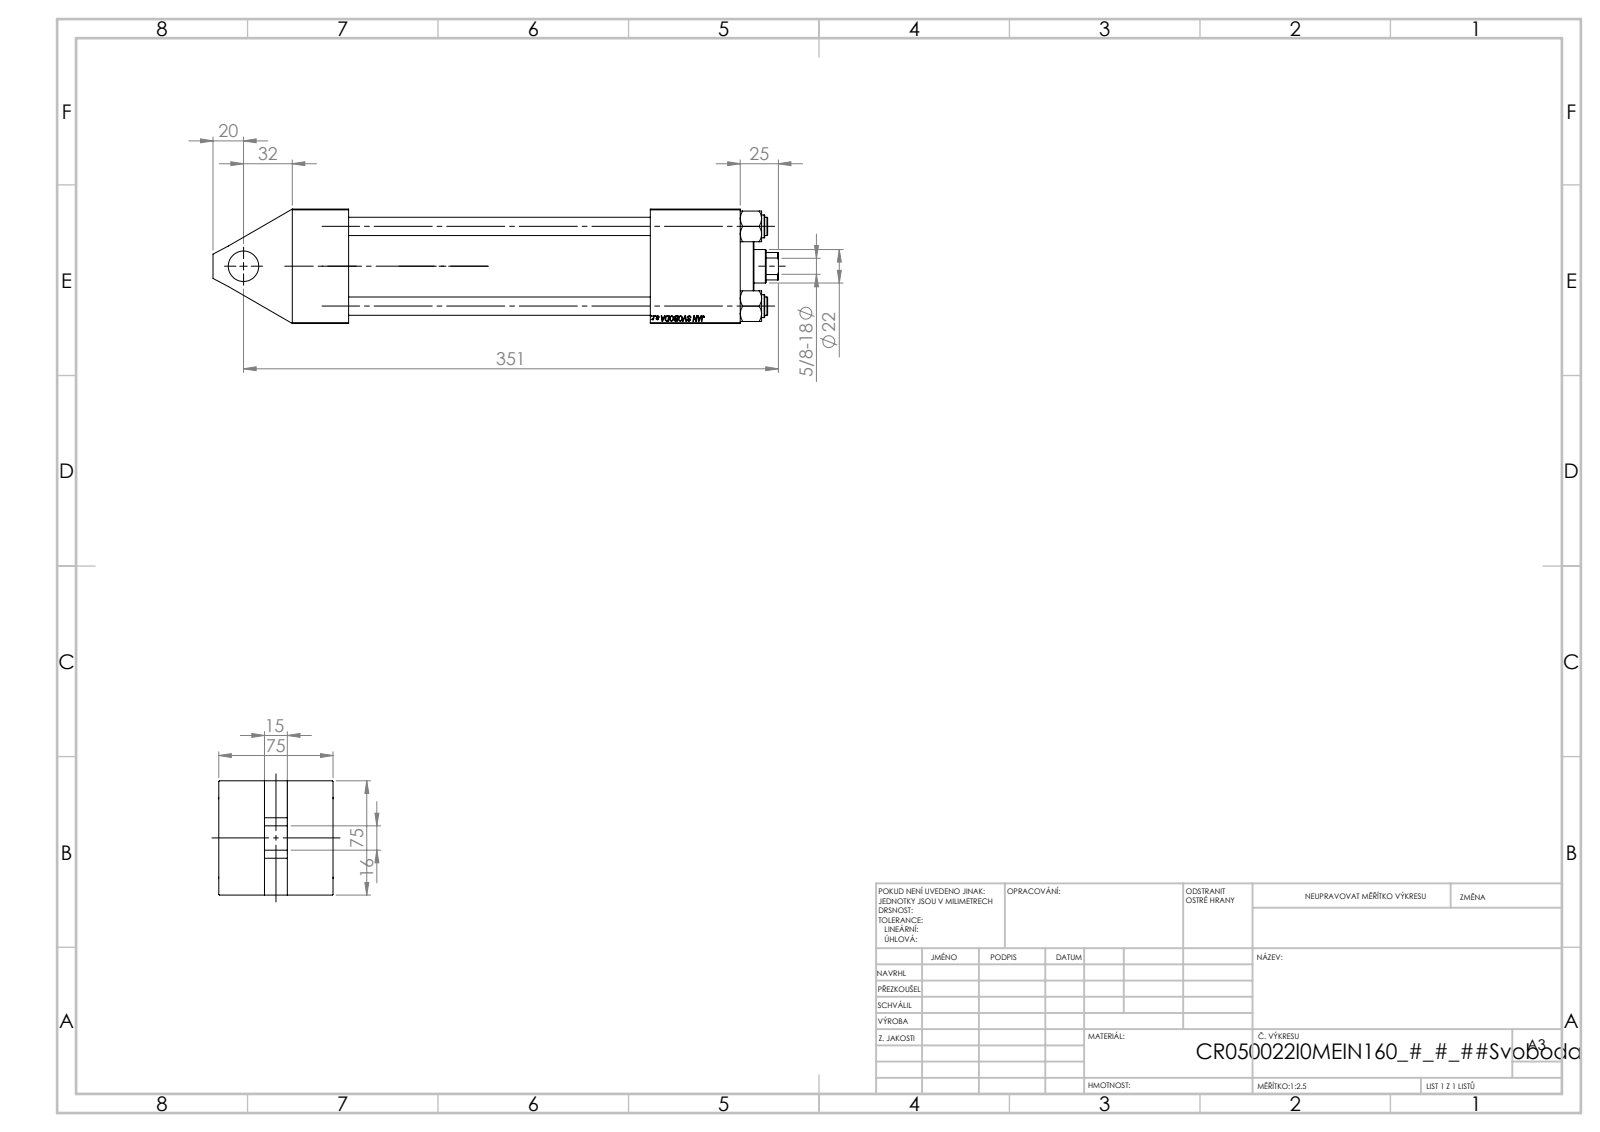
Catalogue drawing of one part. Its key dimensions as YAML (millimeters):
part_name: "V215CR_TYCINKA_I; V215_VC_A; V215CR_I_Body; V215CR_VCP_I (+1 more)"
step_written_by: "SolidWorks 2019 (CONFIG_CONTROL_DESIGN)"
units: millimeters
bodies: {solids: 11, faces: 1078, planar: 502, cylindrical: 80, other: 496}
overall_size: [371, 75.54, 75]
volume: 886523
surface_area: 233590
round_holes:
  - {diameter: 12, count: 4}
  - {diameter: 7, count: 2}
  - {diameter: 20.96, count: 2}
  - {diameter: 30, count: 2}
  - {diameter: 10.5, count: 1}
  - {diameter: 20, count: 1}
  - {diameter: 22, count: 1}
  - {diameter: 25, count: 1}
  - {diameter: 41, count: 1}
  - {diameter: 50, count: 1}
  - {diameter: 53, count: 1}
round_bosses_or_shafts:
  - {diameter: 15, count: 4}
  - {diameter: 56, count: 1}
  - {diameter: 34, count: 1}
partial_cylinders:
  - {radius: 10.5, count: 1}
face_to_face_distances: [75, 257, 37, 294, 45, 30, 235, 198, 59, 265.3]
hole_center_spacings: [36.98, 52.3, 73.96, 233.5]
